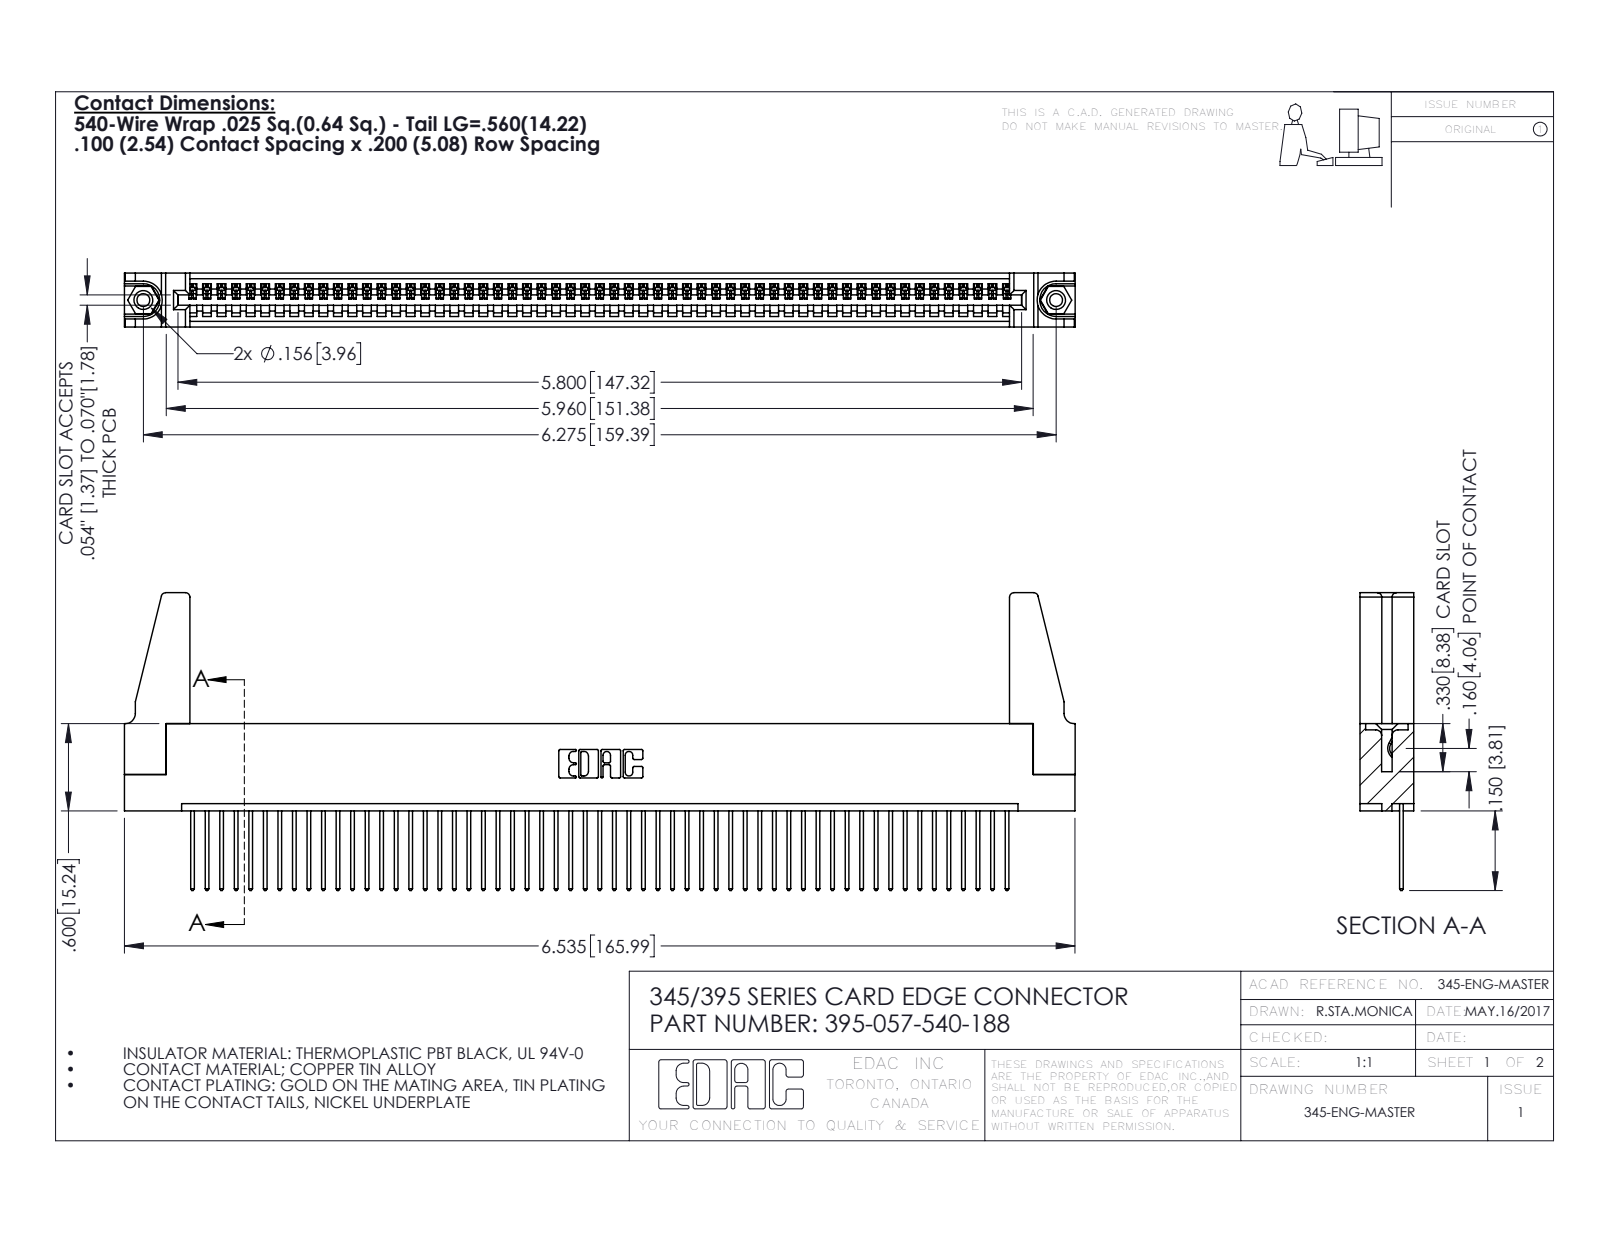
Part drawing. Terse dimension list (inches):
name: 345 Part_Flush Mounting Lugs - 0.156 Dia-TH; 345-220-078_345-220-088; 345-250-001_345-250-001-102; 395-057-540-188 (+1 more)
written by: SolidWorks 2016 (CONFIG_CONTROL_DESIGN)
unit: in
bodies: 62 solids, 3556 faces (2432 planar, 1108 cylindrical, 16 other)
size: 6.536 × 2.047 × 0.37
volume: 1.173 in³; area: 38.92 in²
holes: 2× ⌀0.089, 2× ⌀0.125, 2× ⌀0.156, 1× ⌀0.064
bosses: 2× ⌀0.155
rounds: 114× R0.006, 114× R0.01, 22× R0.01, 8× R0.03, 6× R0.007, 6× R0.031, 3× R0.026, 2× R0.031
face distances: 0.072, 0.298, 0.37, 0.098, 0.272, 0.025, 0.2, 0.225, 0.149, 0.072
hole spacings: 0.27, 6.039, 6.275
